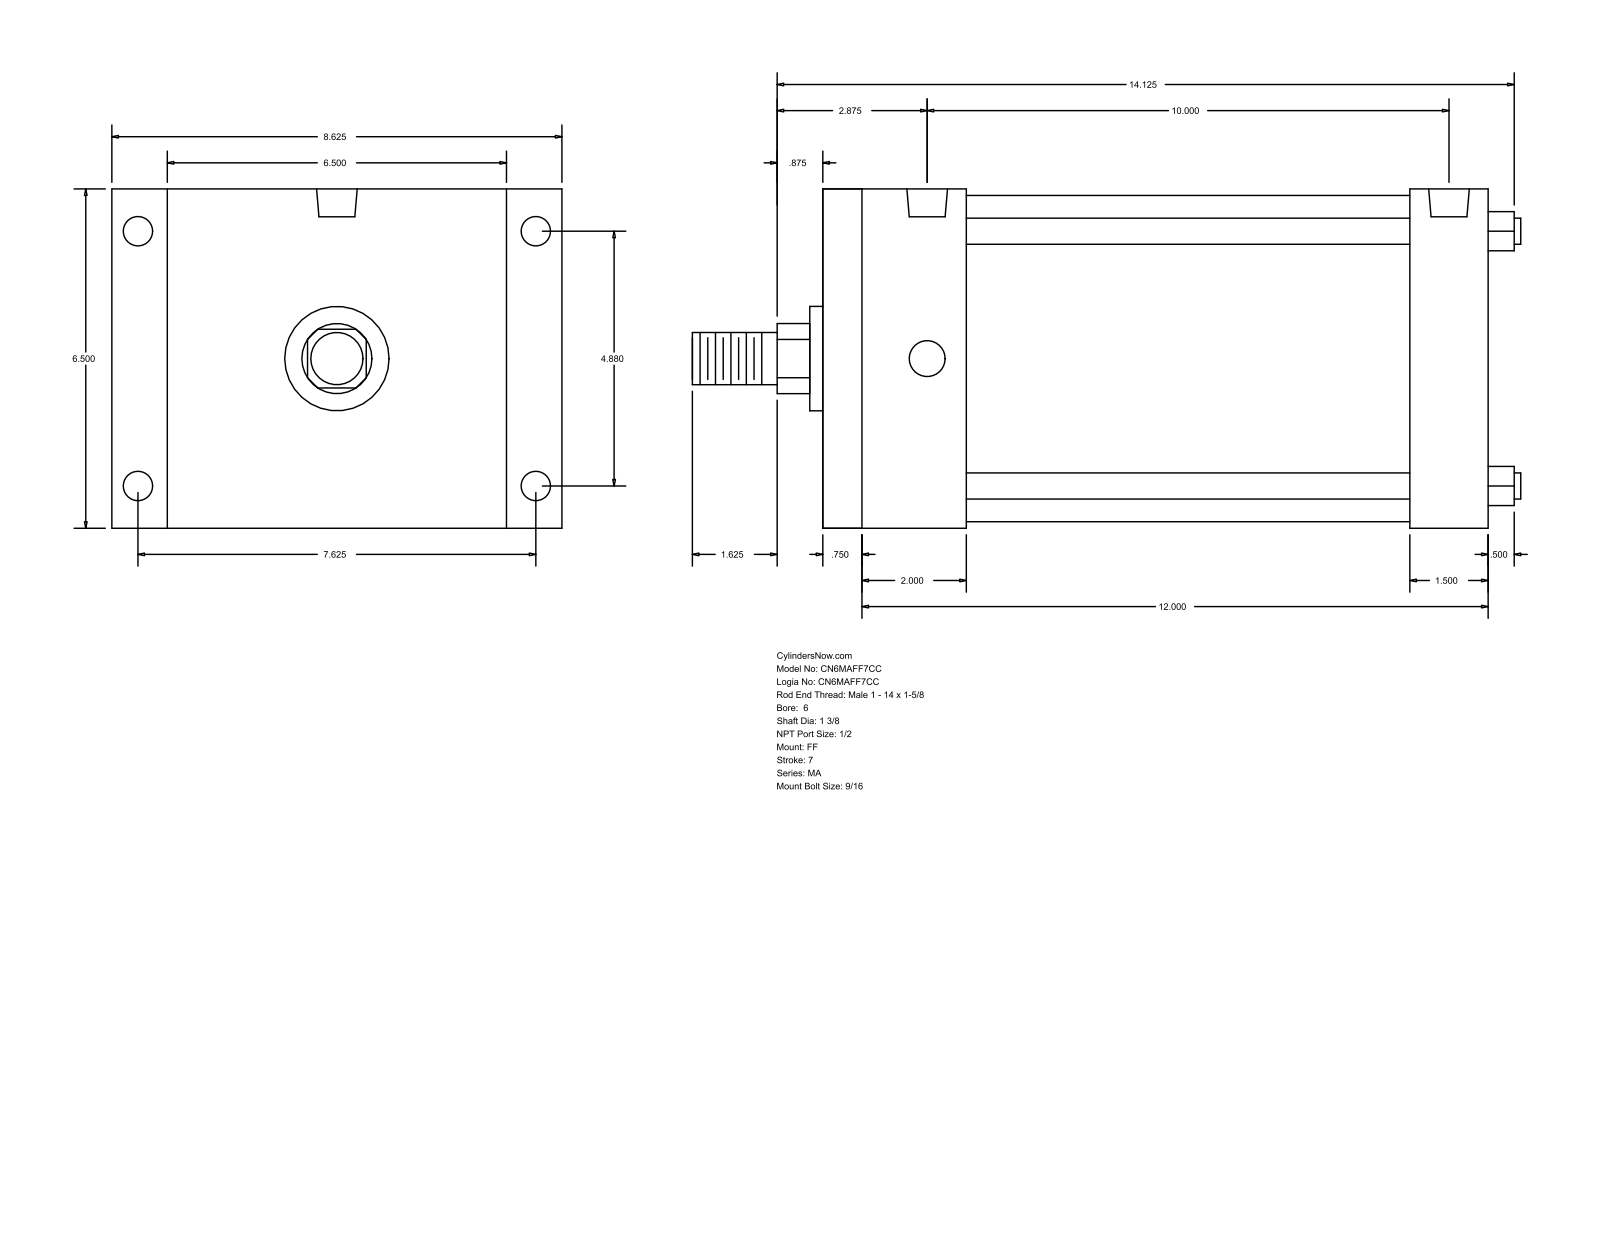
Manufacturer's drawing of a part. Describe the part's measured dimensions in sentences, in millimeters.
The part is named "MA_FF__0600_1.375". Its 3-D file was written by "GSSL Pune (CONFIG_CONTROL_DESIGN)". It is 0 solids with 92 faces: 64 planar, 28 cylindrical and 0 other. Overall it measures 403.23 by 219.07 by 165.1 millimeters. Round holes: 4 of diameter 14.29, 4 of diameter 17.46, 2 of diameter 19.77. Round bosses or shafts: 4 of diameter 12.7, 1 of diameter 158.75, 1 of diameter 50.8, 1 of diameter 34.92, 1 of diameter 25.4. Partial cylindrical surfaces (rounded edges, fillets, slot ends): 1 of radius 17.06. The main face-to-face distances are 165.1, 323.84, 219.08, 15.87, 307.97, 66.67, 50.8, 257.17, 285.75, 269.88. The hole center spacings are 123.96, 193.68, 229.95, 257.17, 3.18, 253.99.
